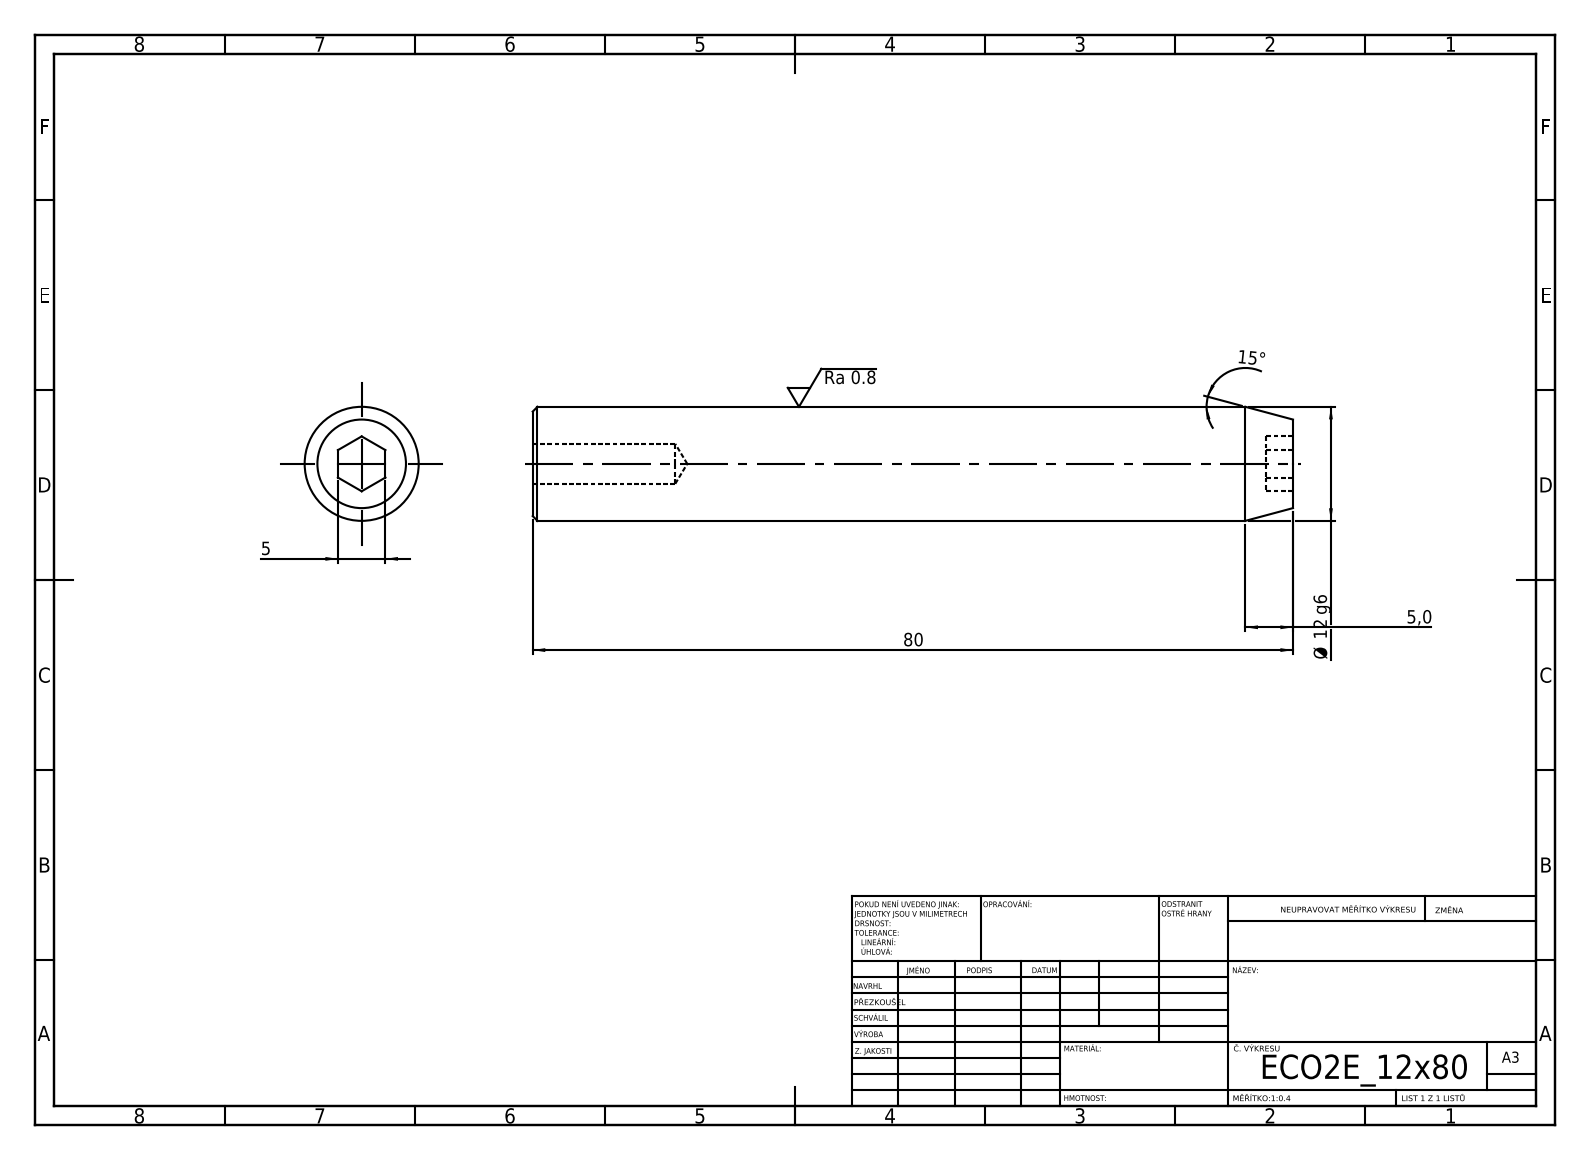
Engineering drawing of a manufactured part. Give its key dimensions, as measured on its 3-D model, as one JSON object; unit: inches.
{"step_written_by": "SolidWorks 2019 (CONFIG_CONTROL_DESIGN)", "units": "inches", "bodies": {"solids": 1, "faces": 19, "planar": 9, "cylindrical": 4, "other": 6}, "overall_size": [3.15, 0.472, 0.472], "volume_in3": 0.528, "surface_area_in2": 5.299, "round_holes": [[0.165, 1]], "round_bosses_or_shafts": [[0.472, 1]], "face_to_face_distances": [3.15, 0.197, 0.11, 3.039]}
